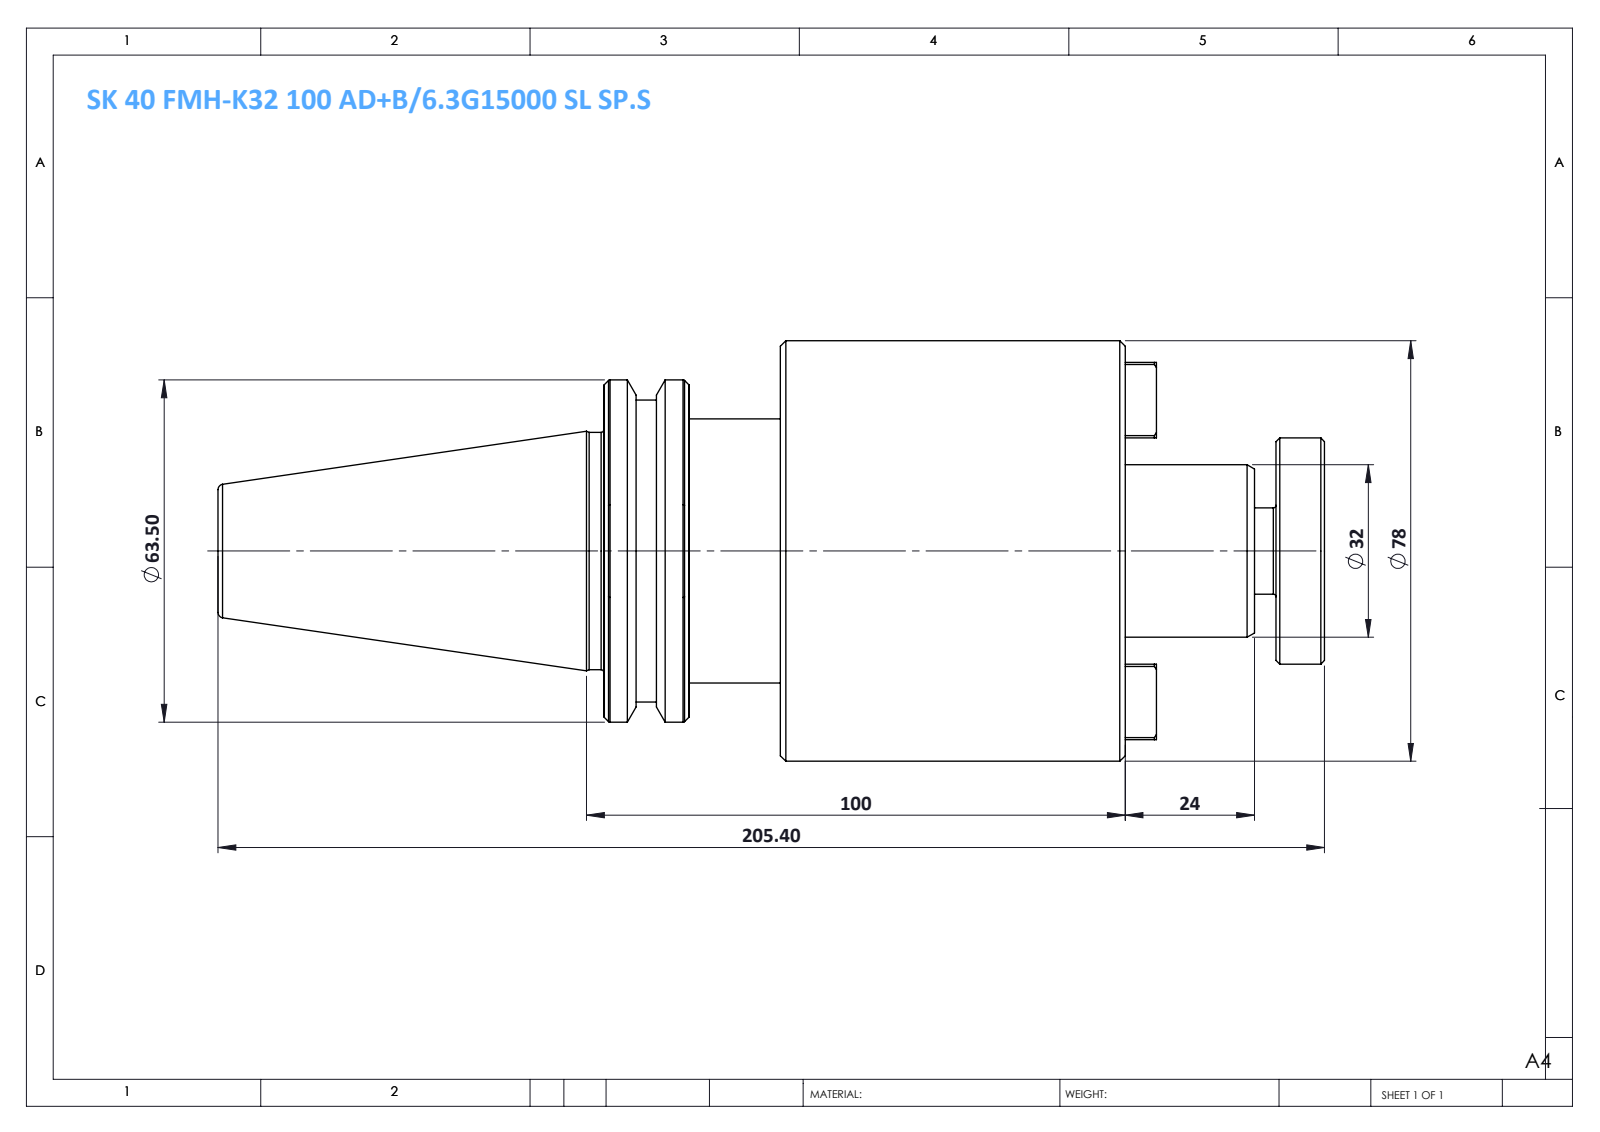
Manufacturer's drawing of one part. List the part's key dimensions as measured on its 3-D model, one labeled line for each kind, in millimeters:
Part name (STEP PRODUCT): SK40 FMH32 100 AD-6.3G15000 SL SP.S
STEP written by: SolidWorks 2014 (CONFIG_CONTROL_DESIGN)
Units: millimetres
Bodies: 1 solid, 110 faces (36 planar, 18 cylindrical, 56 other)
Overall size (bounding box): 205.4 × 78 × 78
Volume: 489 284 mm³ · Surface area: 47 332 mm²
Round bosses / shafts (diameter × count): ⌀78 ×1, ⌀63.5 ×1, ⌀56 ×1, ⌀49 ×1, ⌀44 ×1, ⌀42 ×1, ⌀32 ×1, ⌀16 ×1
Main face-to-face distances: 64, 96.8, 32.8, 37, 101, 133.8, 28, 9, 92, 124.8
